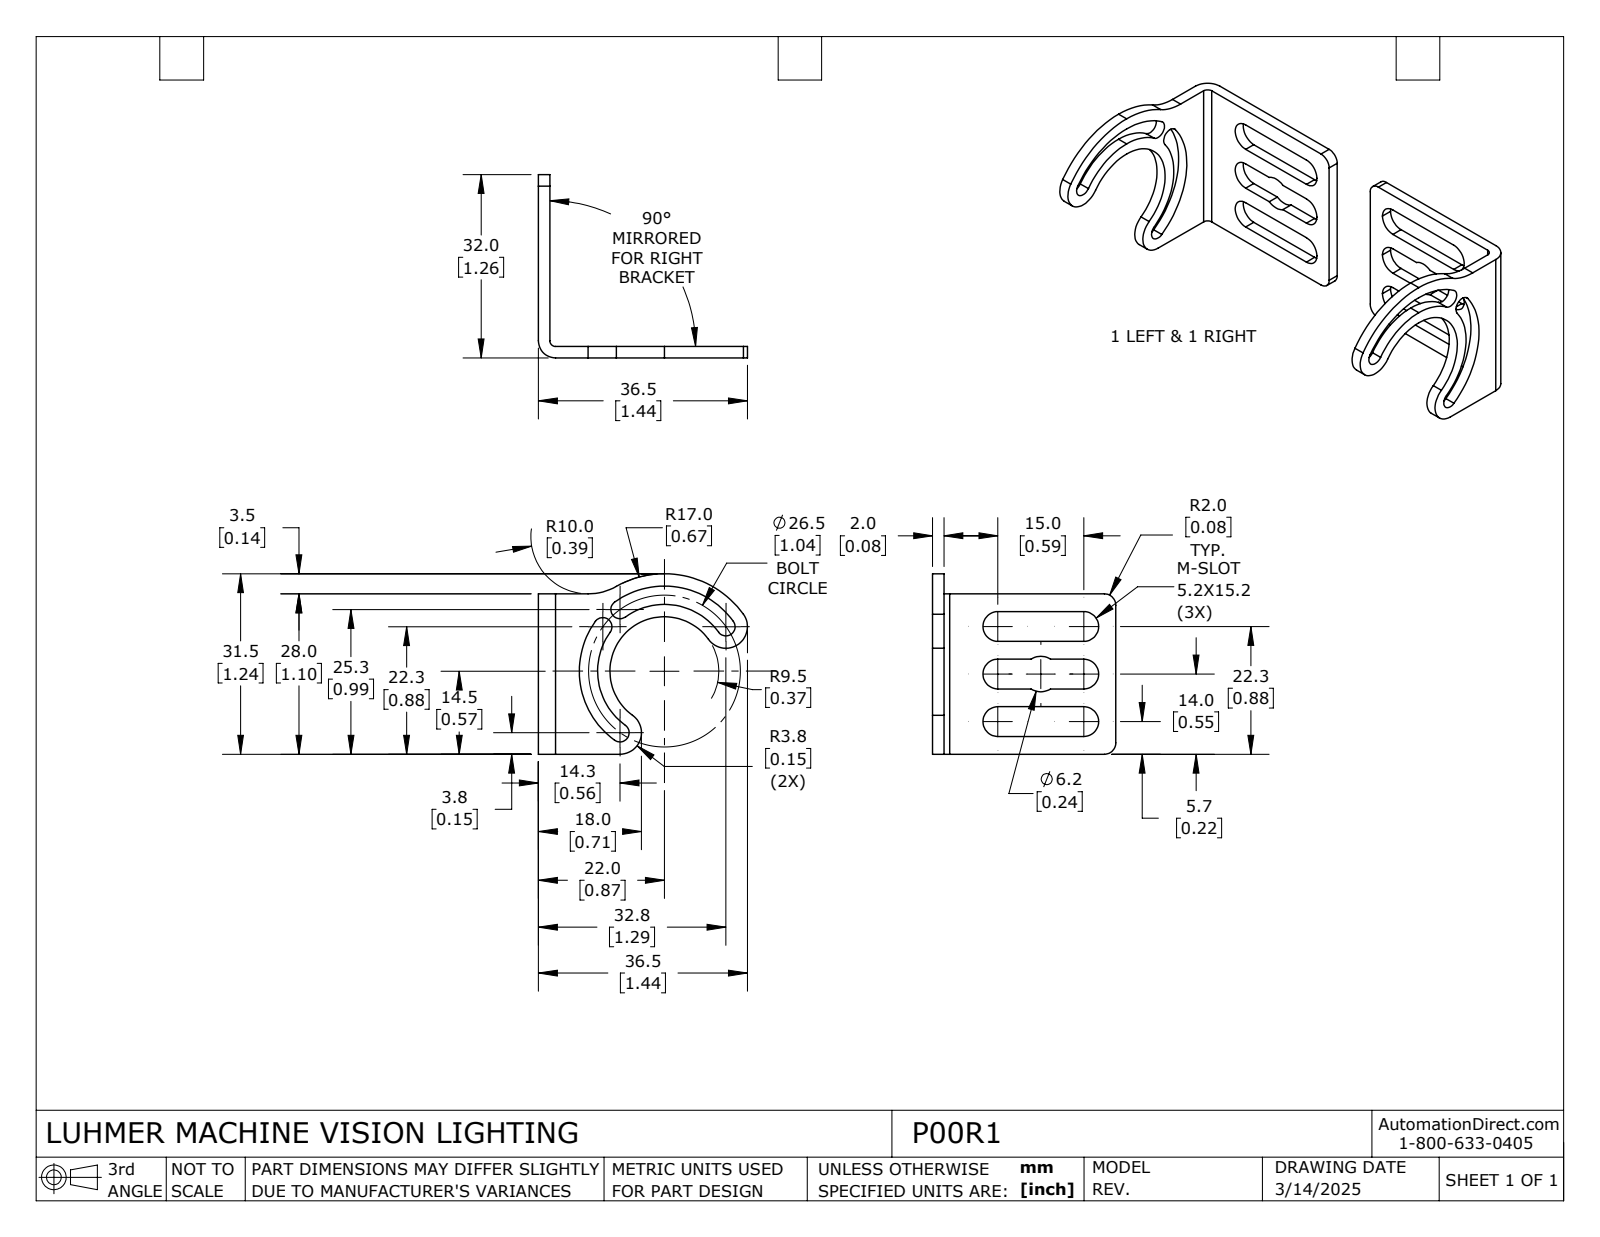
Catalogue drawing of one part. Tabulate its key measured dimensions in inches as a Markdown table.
| quantity | value |
| --- | --- |
| part name | P00R1 |
| STEP written by | SolidWorks 2024 (AUTOMOTIVE_DESIGN) |
| units | inches |
| bodies | 2 solids, 96 faces (30 planar, 66 cylindrical, 0 other) |
| overall size | 2.92 × 1.437 × 1.24 |
| volume | 0.233 in³ |
| surface area | 8.621 in² |
| partial cylindrical surfaces (radius × count) | 0.102 × 12, 0.063 × 4, 0.079 × 4, 0.039 × 2, 0.118 × 2, 0.122 × 2, 0.148 × 2, 0.374 × 1 |
| main face-to-face distances | 0.079, 2.841, 2.92, 2.762, 0.327, 0.122, 0.654, 0.205, 0.449, 1.102 |
